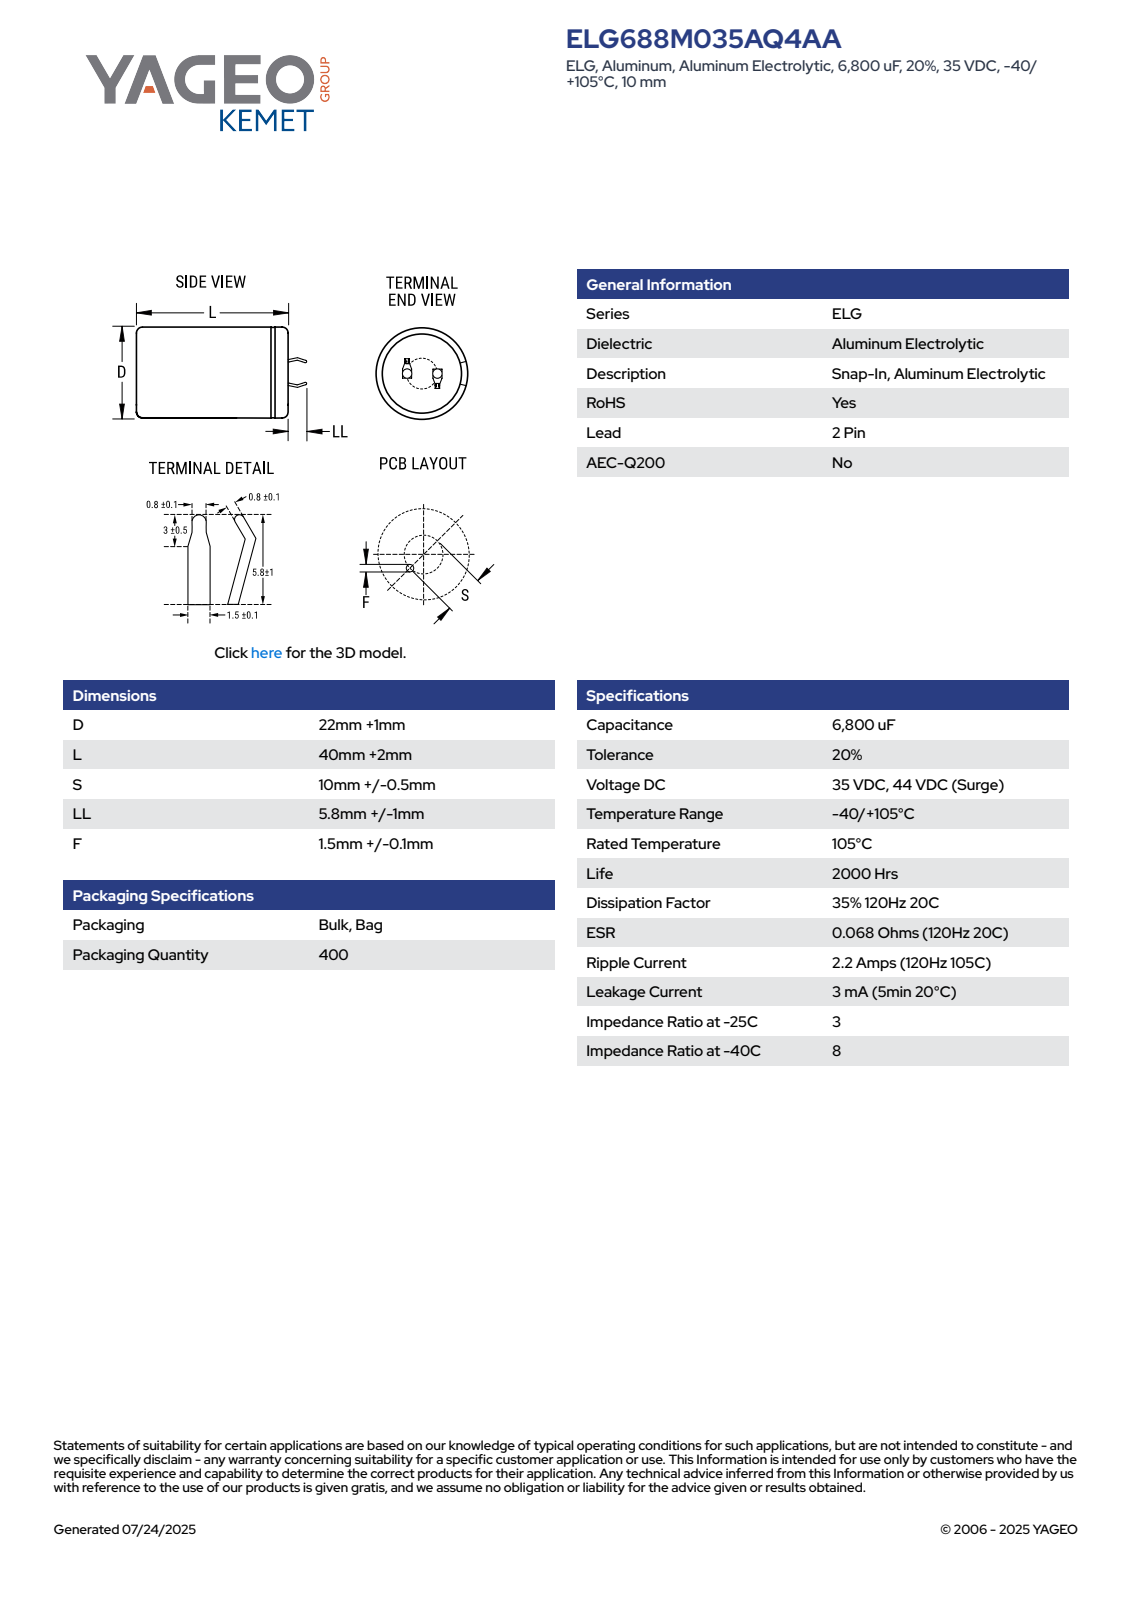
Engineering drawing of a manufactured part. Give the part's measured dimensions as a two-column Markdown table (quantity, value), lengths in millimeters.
| quantity | value |
| --- | --- |
| part name | CARS_K2P_22X40_D23L42S10LL6.8F1.6 |
| STEP written by | SolidWorks 2014 (AUTOMOTIVE_DESIGN) |
| units | millimeters |
| bodies | 1 solid, 100 faces (52 planar, 9 cylindrical, 39 other) |
| overall size | 48.79 × 23 × 23 |
| volume | 17 320 mm³ |
| surface area | 3 890 mm² |
| round holes (diameter × count) | 20.35 × 1 |
| round bosses / shafts (diameter × count) | 23 × 1 |
| partial cylindrical surfaces (radius × count) | 11.49 × 1 |
| main face-to-face distances | 41.99, 0.6, 42.49, 0.5, 7.08, 7.63, 0.75, 1.35, 7.68, 6.48 |
